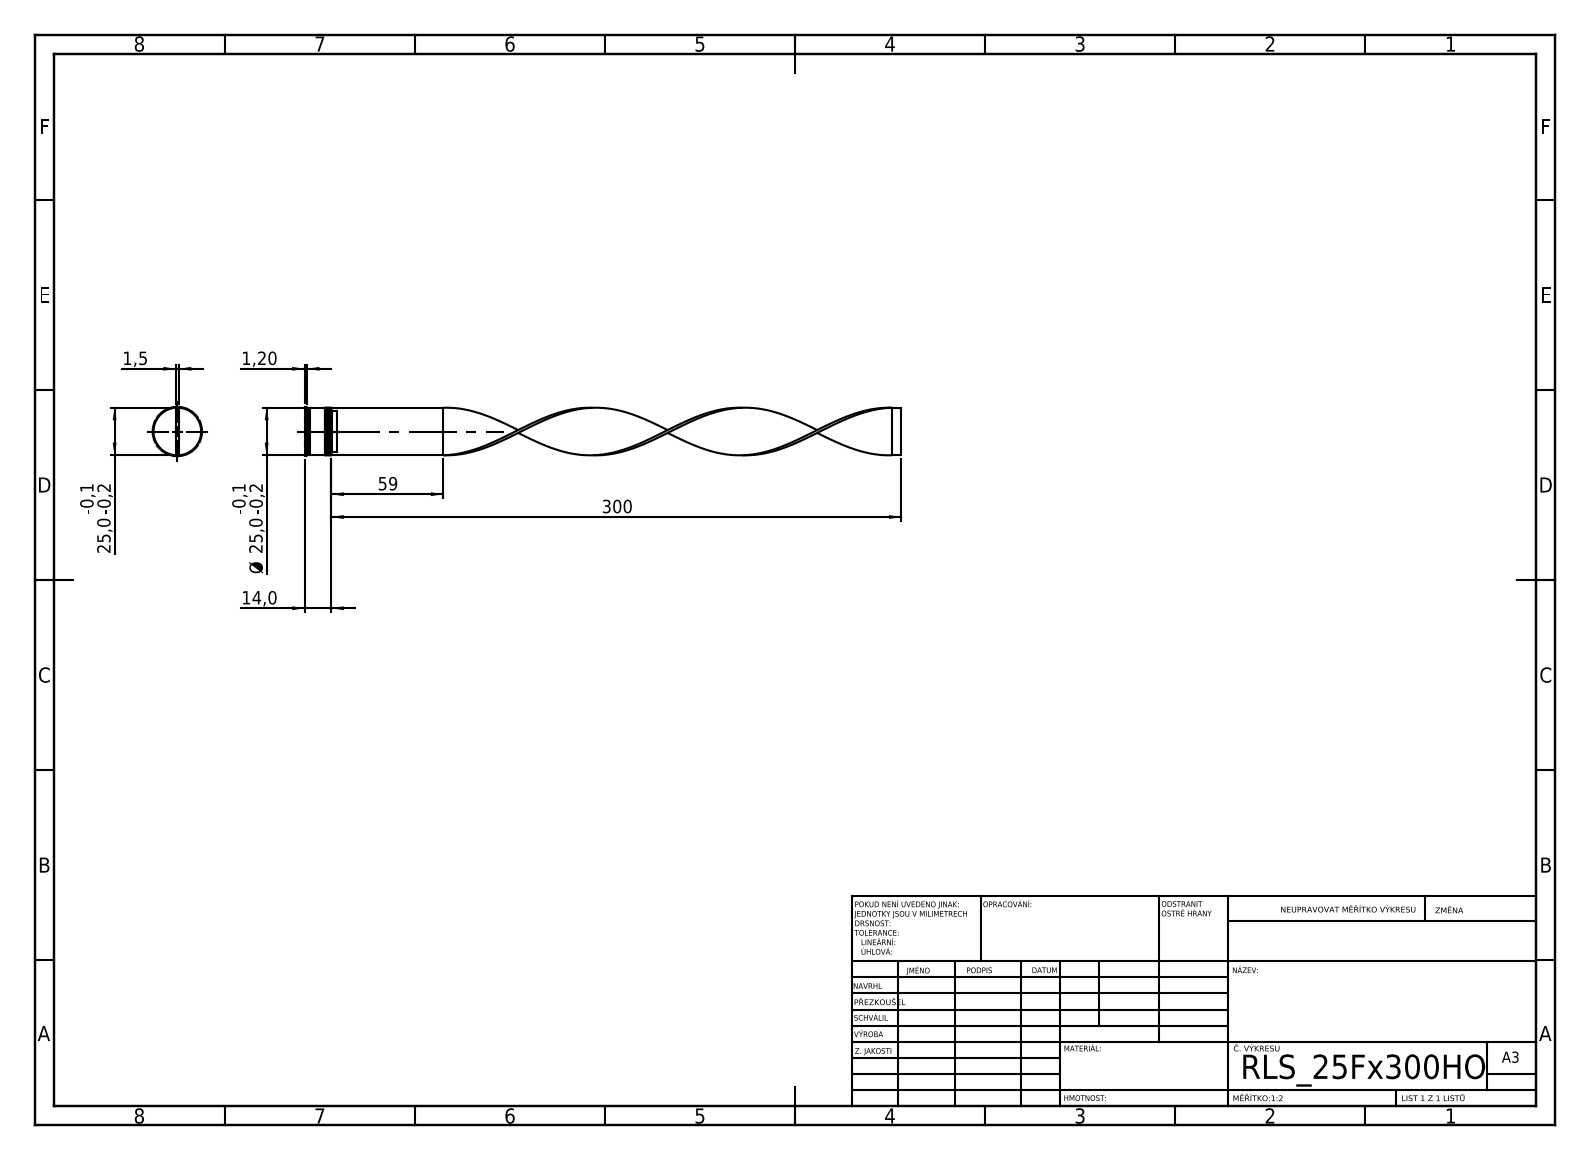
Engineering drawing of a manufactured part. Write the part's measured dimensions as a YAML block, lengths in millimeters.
step_written_by: "SolidWorks 2019 (CONFIG_CONTROL_DESIGN)"
units: millimeters
bodies: {solids: 3, faces: 108, planar: 48, cylindrical: 33, other: 27}
overall_size: [314, 26, 25.98]
volume: 19377
surface_area: 20820
round_bosses_or_shafts:
  - {diameter: 26, count: 1}
  - {diameter: 25, count: 1}
  - {diameter: 24.4, count: 1}
  - {diameter: 21.8, count: 1}
partial_cylinders:
  - {radius: 11, count: 1}
face_to_face_distances: [1.5, 0.7, 2.2, 0.8, 11.7, 11, 10.2, 9.5, 4.3, 5]
